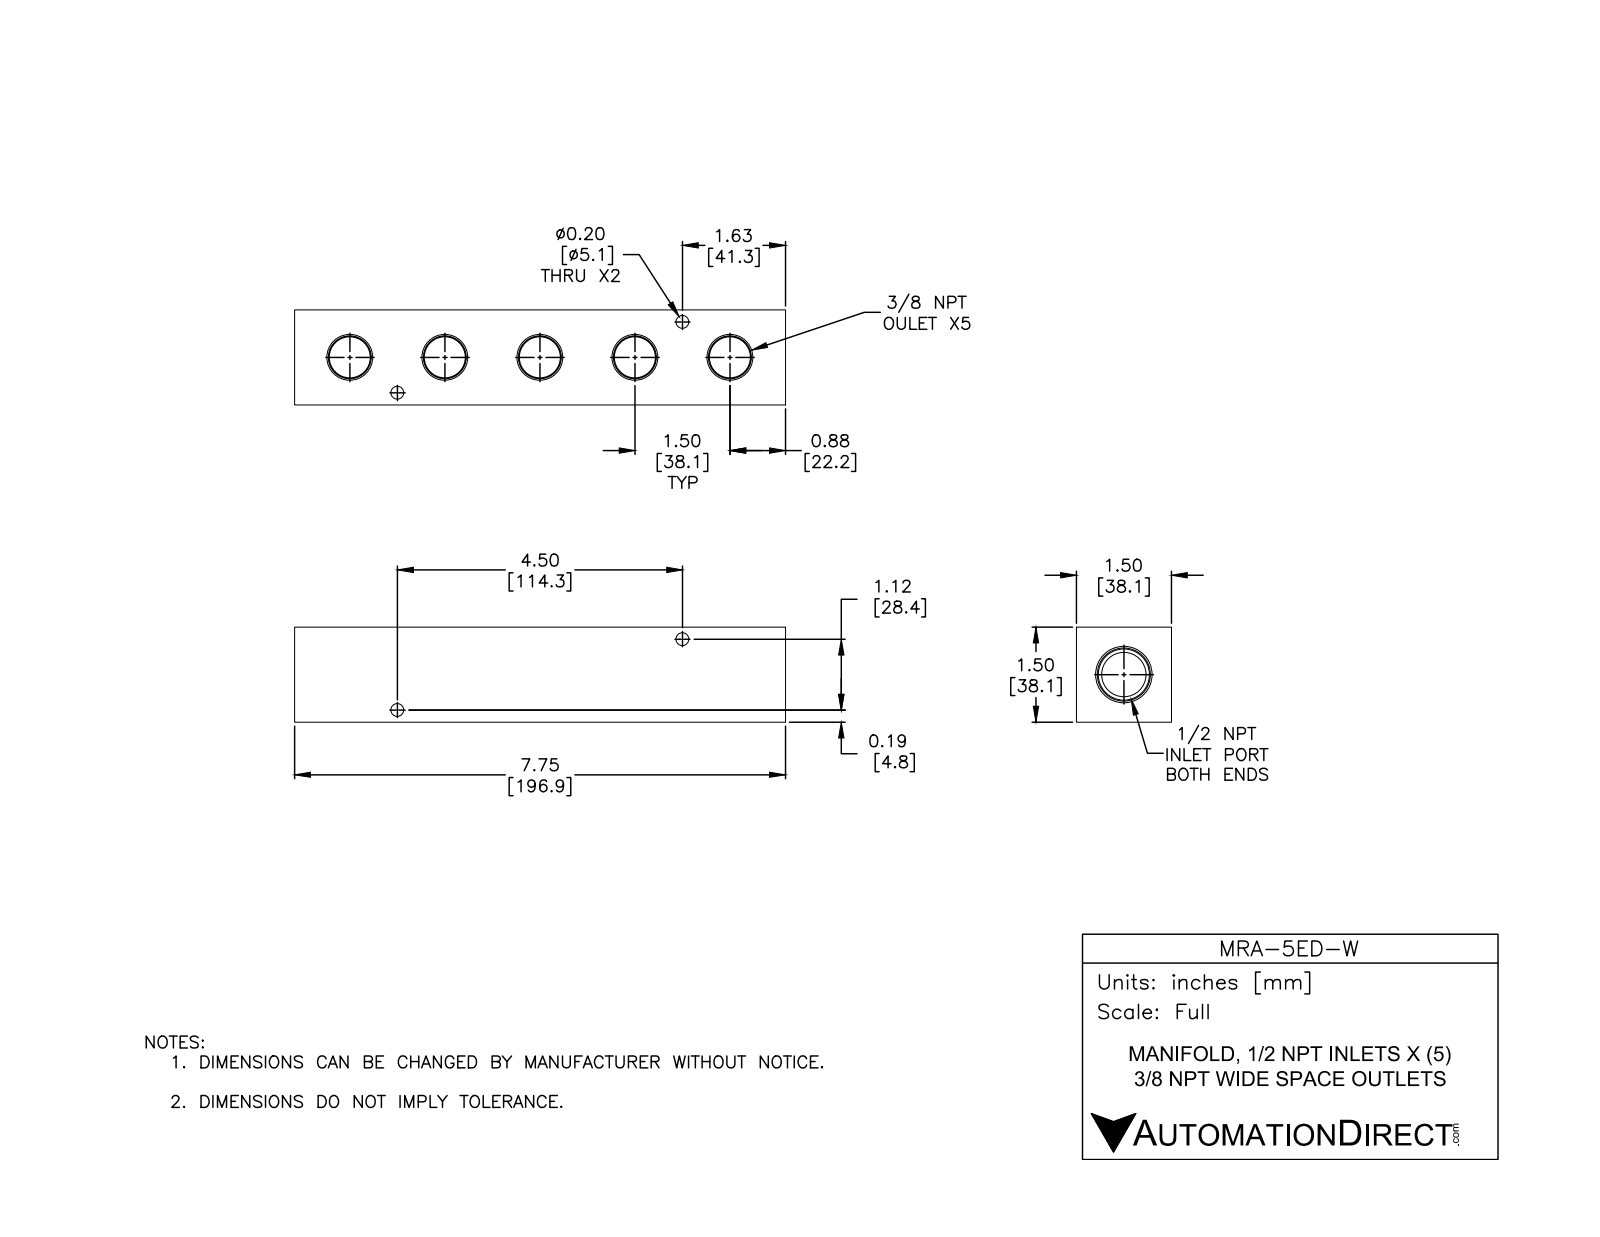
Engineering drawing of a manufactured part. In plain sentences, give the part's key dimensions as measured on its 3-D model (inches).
The part is named "MRA-5ED-W". Its 3-D file was written by "SolidWorks 2015 (CONFIG_CONTROL_DESIGN)". It is 1 solid with 74 faces: 18 planar, 28 cylindrical and 28 other. Overall it measures 7.75 by 1.5 by 1.5 inches. Its volume is 13.36 cubic inches and its surface area 72.5 square inches. Round holes: 5 of diameter 0.562, 4 of diameter 0.2, 1 of diameter 0.703. The main face-to-face distances are 1.5, 7.75, 1.09, 0.41, 0.53, 7.22, 6.69. The hole center spacings are 1.5, 3, 0.932, 0.94, 4.5, 4.637, 2.314, 2.324.
